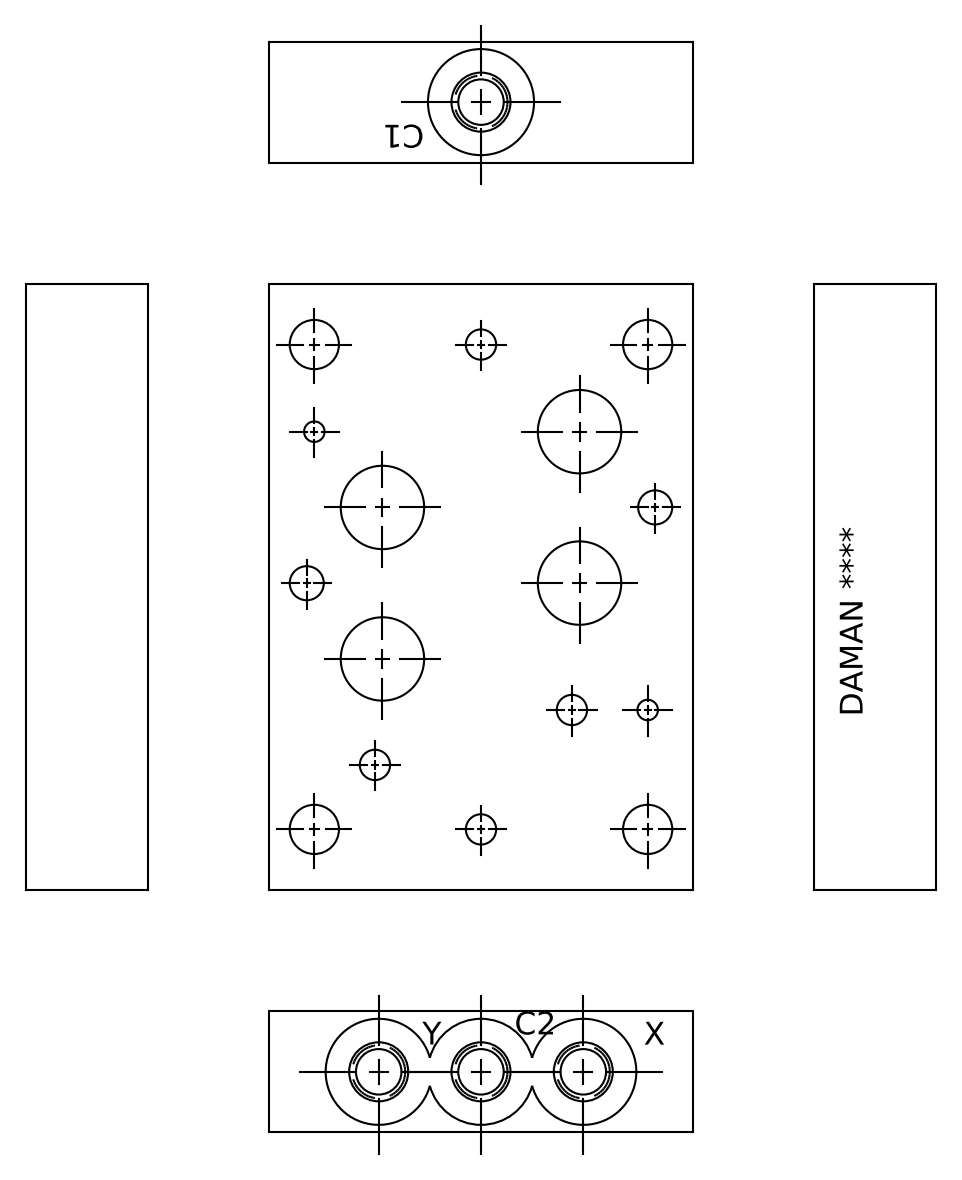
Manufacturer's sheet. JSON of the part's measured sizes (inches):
{"part_name": "Part_AD07TPXY4S_3D", "step_written_by": "Autodesk Inventor 2021 (AUTOMOTIVE_DESIGN)", "units": "inches", "bodies": {"solids": 1, "faces": 478, "planar": 310, "cylindrical": 48, "other": 120}, "overall_size": [5, 3.5, 1], "volume_in3": 14.49, "surface_area_in2": 70.72, "round_holes": [[0.438, 7], [0.25, 4], [0.406, 4], [0.688, 4], [1, 4], [0.375, 3], [0.838, 3], [0.125, 2], [0.172, 2], [0.197, 2], [0.236, 2], [0.389, 2]], "partial_cylinders_radius": [[0.194, 1]], "face_to_face_distances": [1, 3.5, 5, 0.11, 0.89, 0.031, 4.969, 0.052, 0.058, 0.948], "hole_center_spacings": [1.741, 4, 0.844, 0.884, 0.884, 1.25, 1.375, 1.375]}
